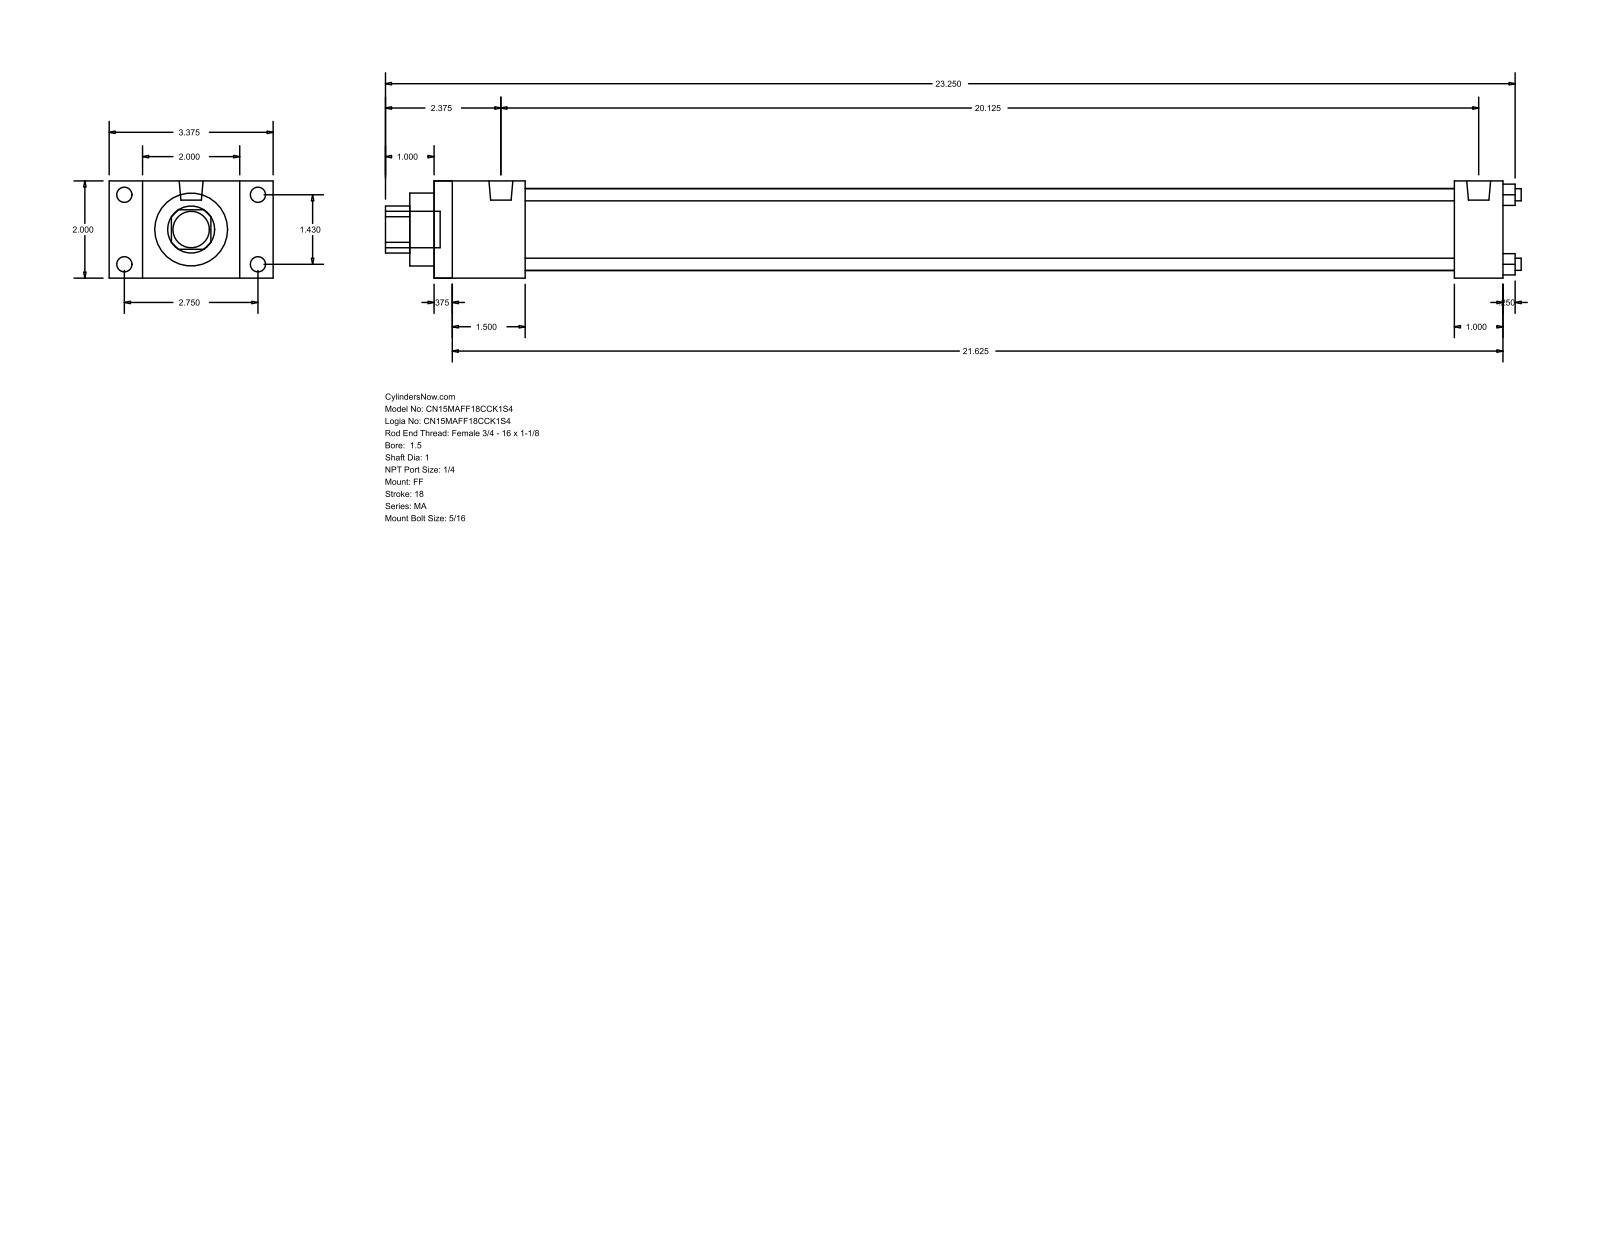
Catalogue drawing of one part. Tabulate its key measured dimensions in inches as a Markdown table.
| quantity | value |
| --- | --- |
| part name | MA_FF__0150_1 |
| STEP written by | GSSL Pune (CONFIG_CONTROL_DESIGN) |
| units | inches |
| bodies | 0 solids, 92 faces (64 planar, 28 cylindrical, 0 other) |
| overall size | 23.375 × 3.375 × 2 |
| round holes (diameter × count) | 0.25 × 4, 1 × 1, 1.5 × 1, 1.69 × 1 |
| round bosses / shafts (diameter × count) | 0.313 × 8, 0.492 × 2, 0.75 × 1 |
| partial cylindrical surfaces (radius × count) | 0.484 × 1 |
| main face-to-face distances | 2, 22, 0.375, 21.625, 1, 1.875, 21, 1.5, 20.625, 19.125 |
| hole center spacings | 1.011, 1.43, 2.022 |
